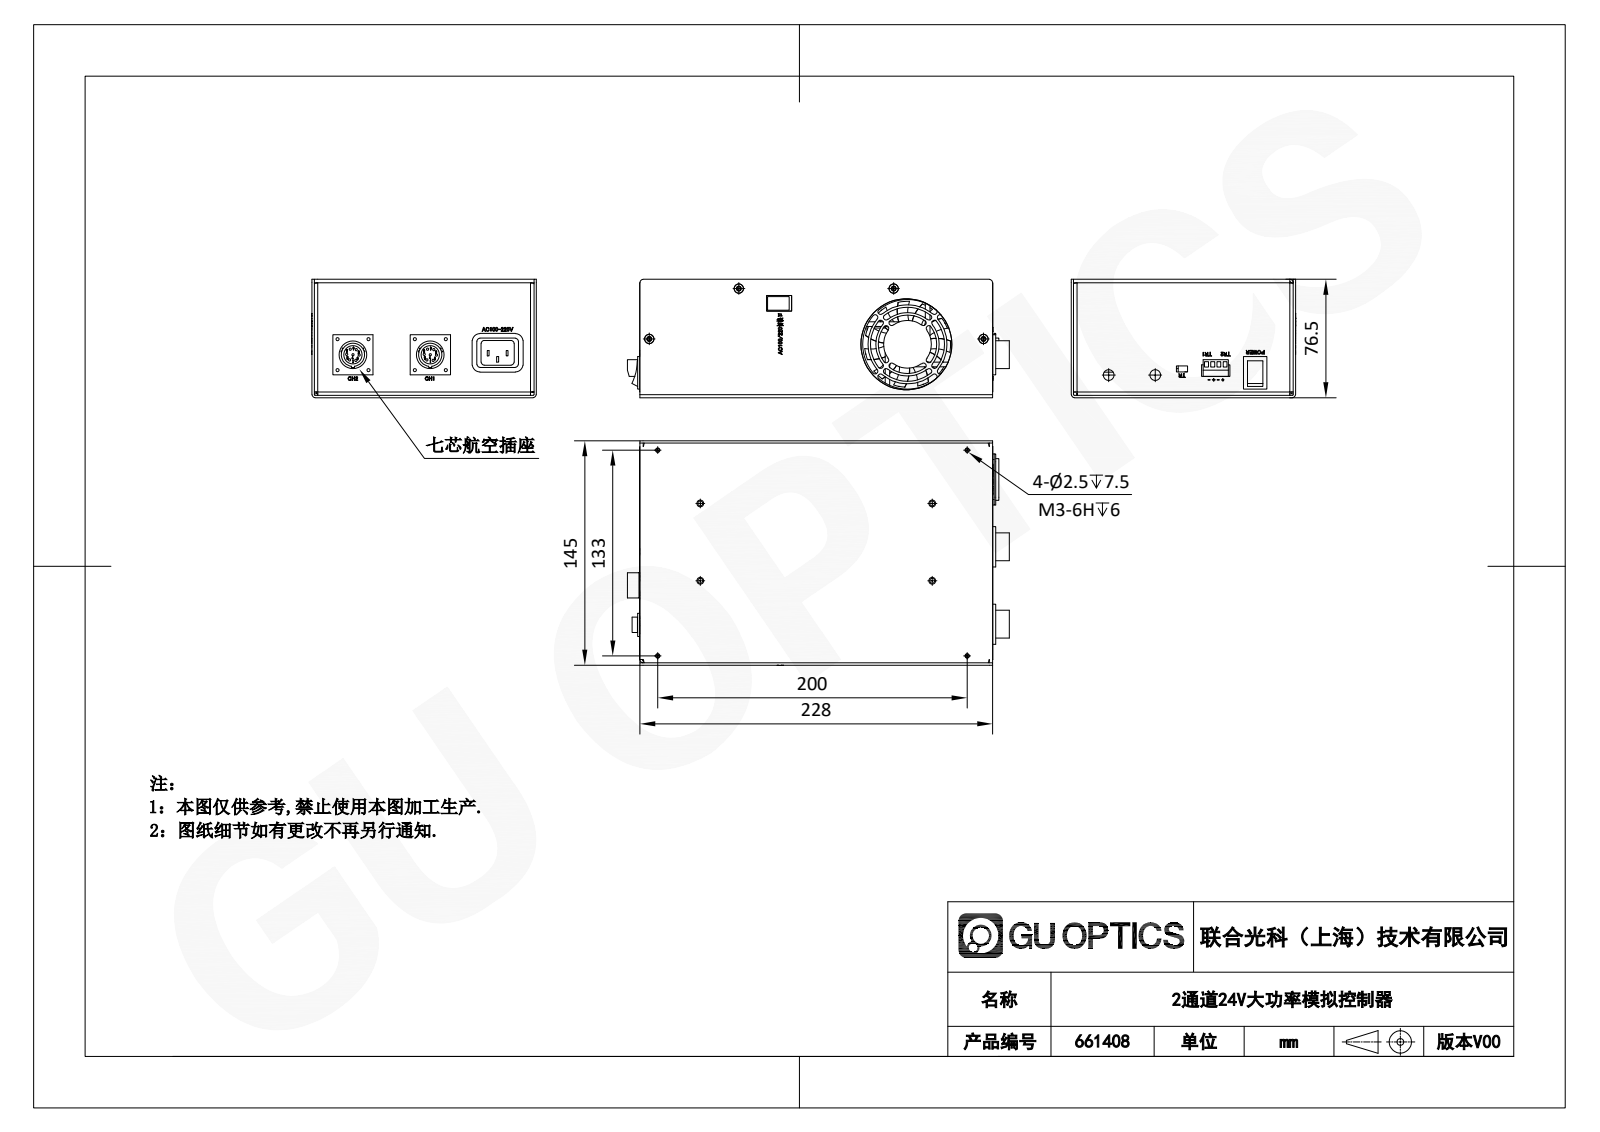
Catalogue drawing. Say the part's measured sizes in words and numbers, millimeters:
The part is named "661408". Its 3-D file was written by "SolidWorks 2020 (CONFIG_CONTROL_DESIGN)". It is 15 solids with 2471 faces: 1341 planar, 442 cylindrical and 688 other. Overall it measures 246.8 by 145.1 by 76.5 millimeters. Its volume is 1 023 000 cubic millimeters and its surface area 549 693 square millimeters. Round holes: 31 of diameter 2.5, 14 of diameter 1.5, 10 of diameter 2.3, 5 of diameter 3.3, 4 of diameter 3.2, 4 of diameter 4.5, 4 of diameter 4.6, 4 of diameter 6.3, 2 of diameter 3.5, 2 of diameter 7.2, 2 of diameter 15, 2 of diameter 18. Round bosses or shafts: 2 of diameter 12, 1 of diameter 51, 1 of diameter 41, 1 of diameter 28, 1 of diameter 2. Partial cylindrical surfaces (rounded edges, fillets, slot ends): 52 of radius 1.5, 18 of radius 2, 10 of radius 0.74, 10 of radius 2.24, 8 of radius 1.76, 8 of radius 1.76, 8 of radius 1.77, 6 of radius 4. The main face-to-face distances are 1.5, 75, 142, 143.5, 73.5, 76.5, 3, 30, 27.5, 45. The hole center spacings are 50, 4.01, 6.93, 4, 14.14, 20, 3.99, 8.
